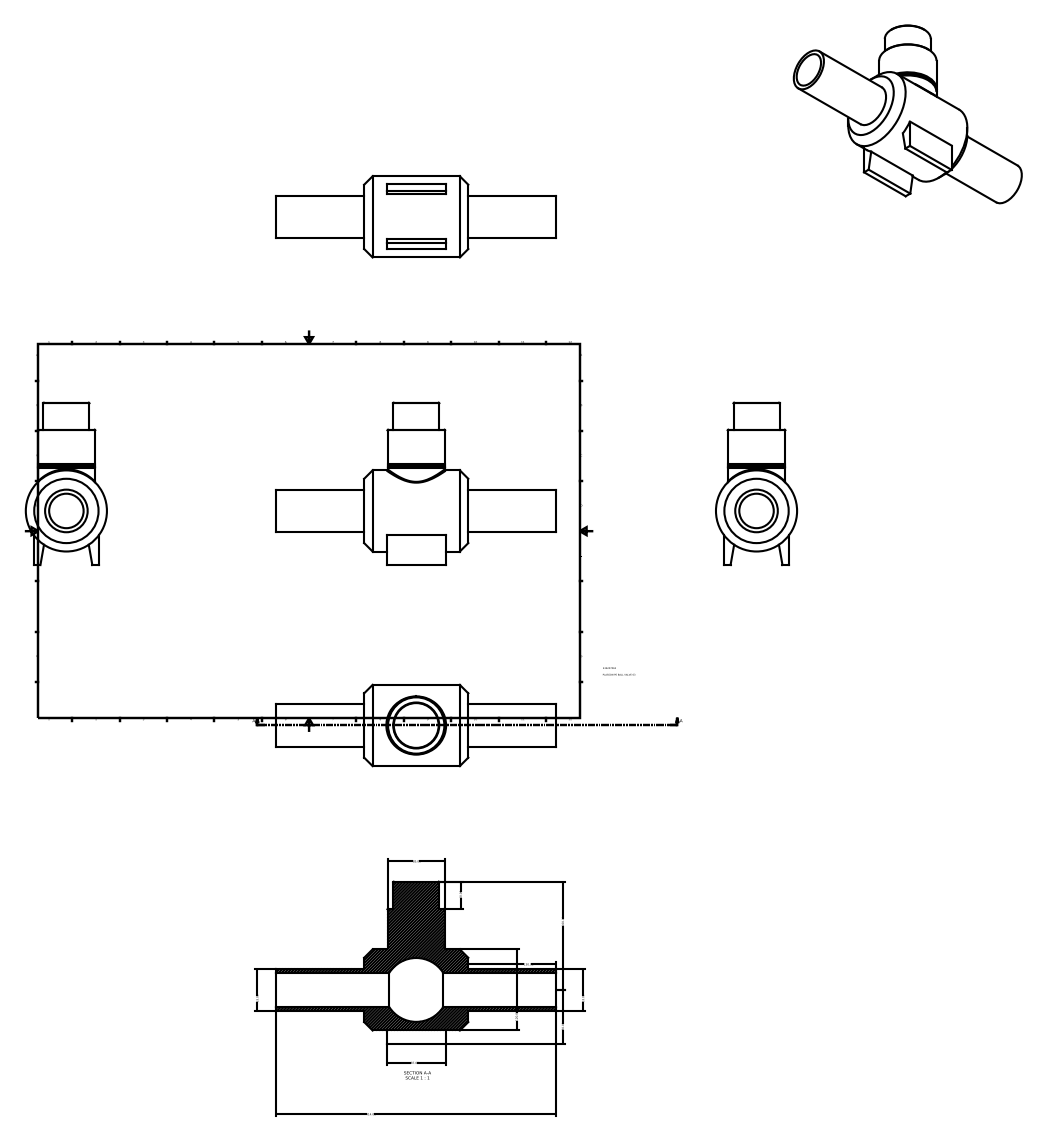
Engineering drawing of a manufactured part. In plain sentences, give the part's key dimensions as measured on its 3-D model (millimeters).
The part is named "436207063". Its 3-D file was written by "Autodesk Inventor 2015 (AUTOMOTIVE_DESIGN)". It is 1 solid with 33 faces: 16 planar, 9 cylindrical and 8 other. Overall it measures 414 by 240 by 120 millimeters. Its volume is 1 977 000 cubic millimeters and its surface area 238 786 square millimeters. Round holes: 1 of diameter 51. Round bosses or shafts: 1 of diameter 120, 1 of diameter 85, 1 of diameter 68, 1 of diameter 63. The main face-to-face distances are 154, 96, 130, 284, 163.5, 250.5, 33.5, 120.5, 40, 200.
